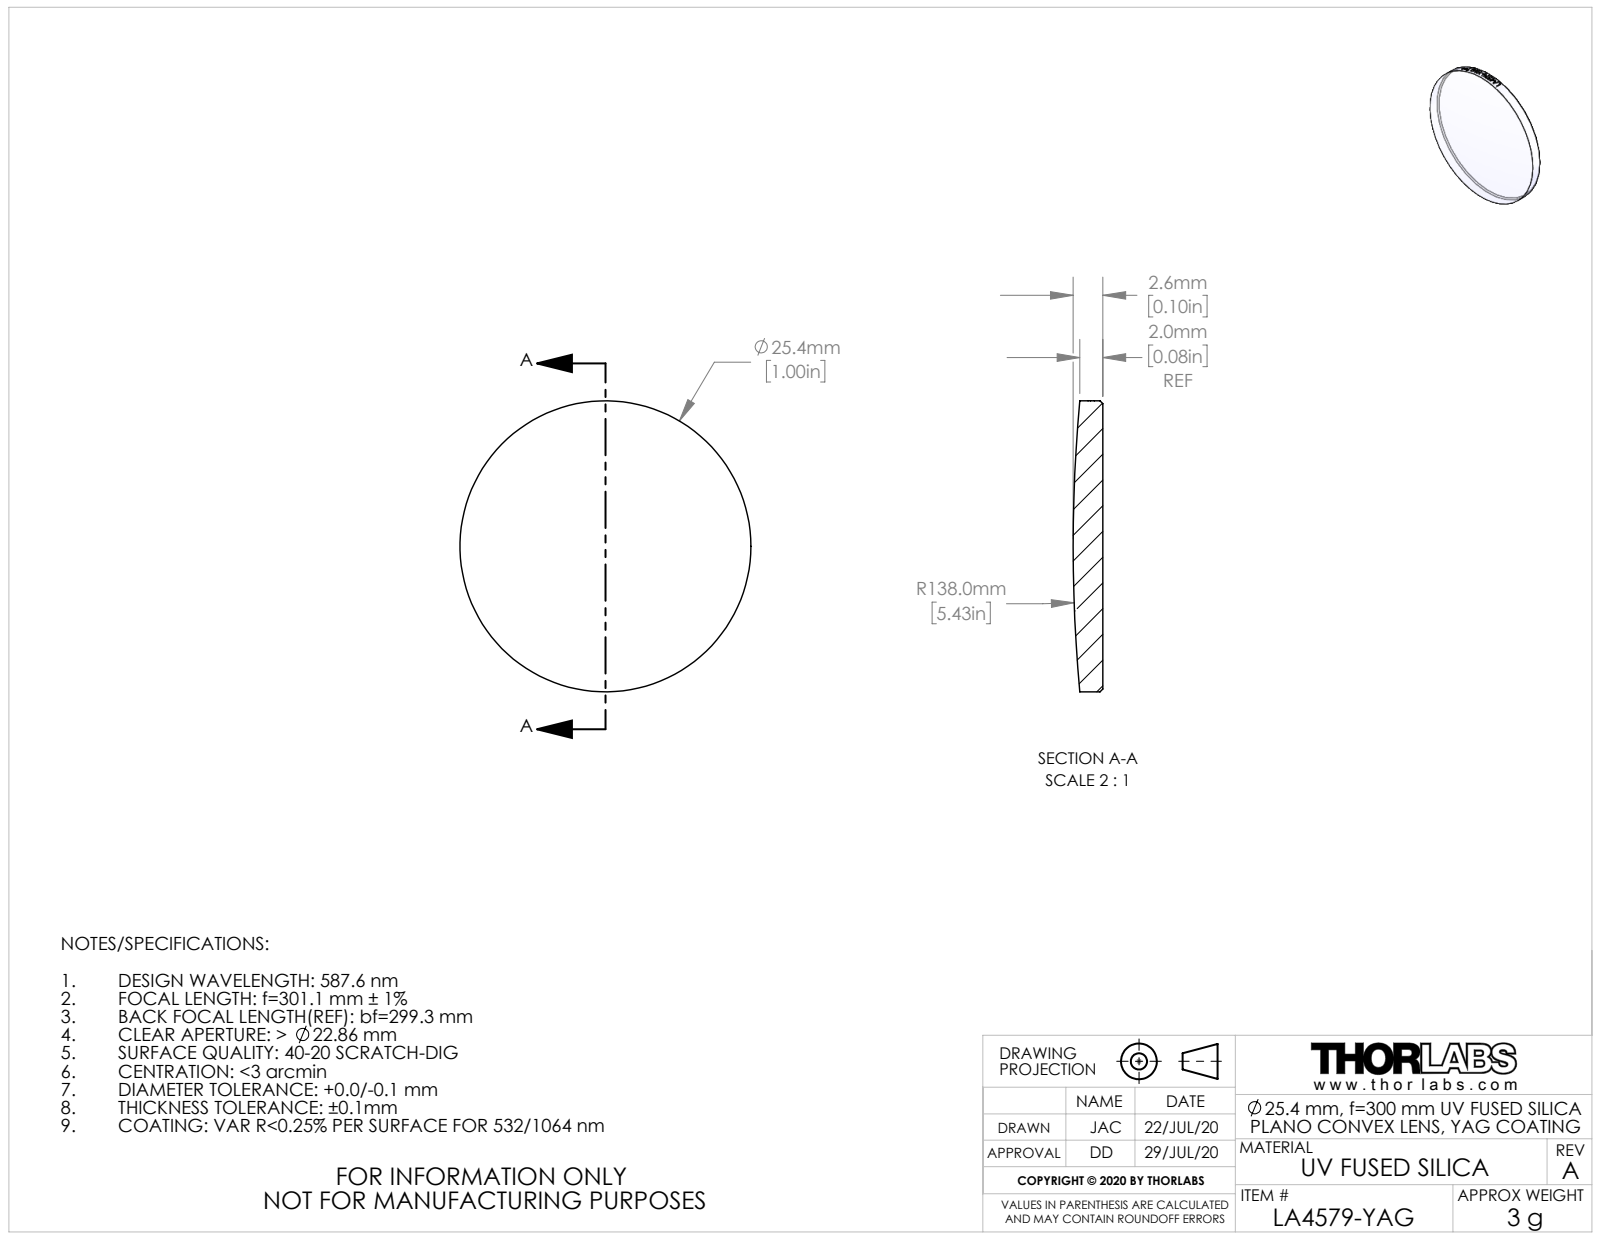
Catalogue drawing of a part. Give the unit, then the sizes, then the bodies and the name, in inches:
Units: inches
Overall size (bounding box): 1 × 1 × 0.102
Round bosses / shafts (diameter × count): ⌀1 ×1
Volume: 0.071 in³ · Surface area: 1.803 in²
Bodies: 1 solid, 25 faces (1 planar, 20 cylindrical, 4 other)
Part name (STEP PRODUCT): TTN217853-E0W
STEP written by: SolidWorks 2018 (CONFIG_CONTROL_DESIGN)
